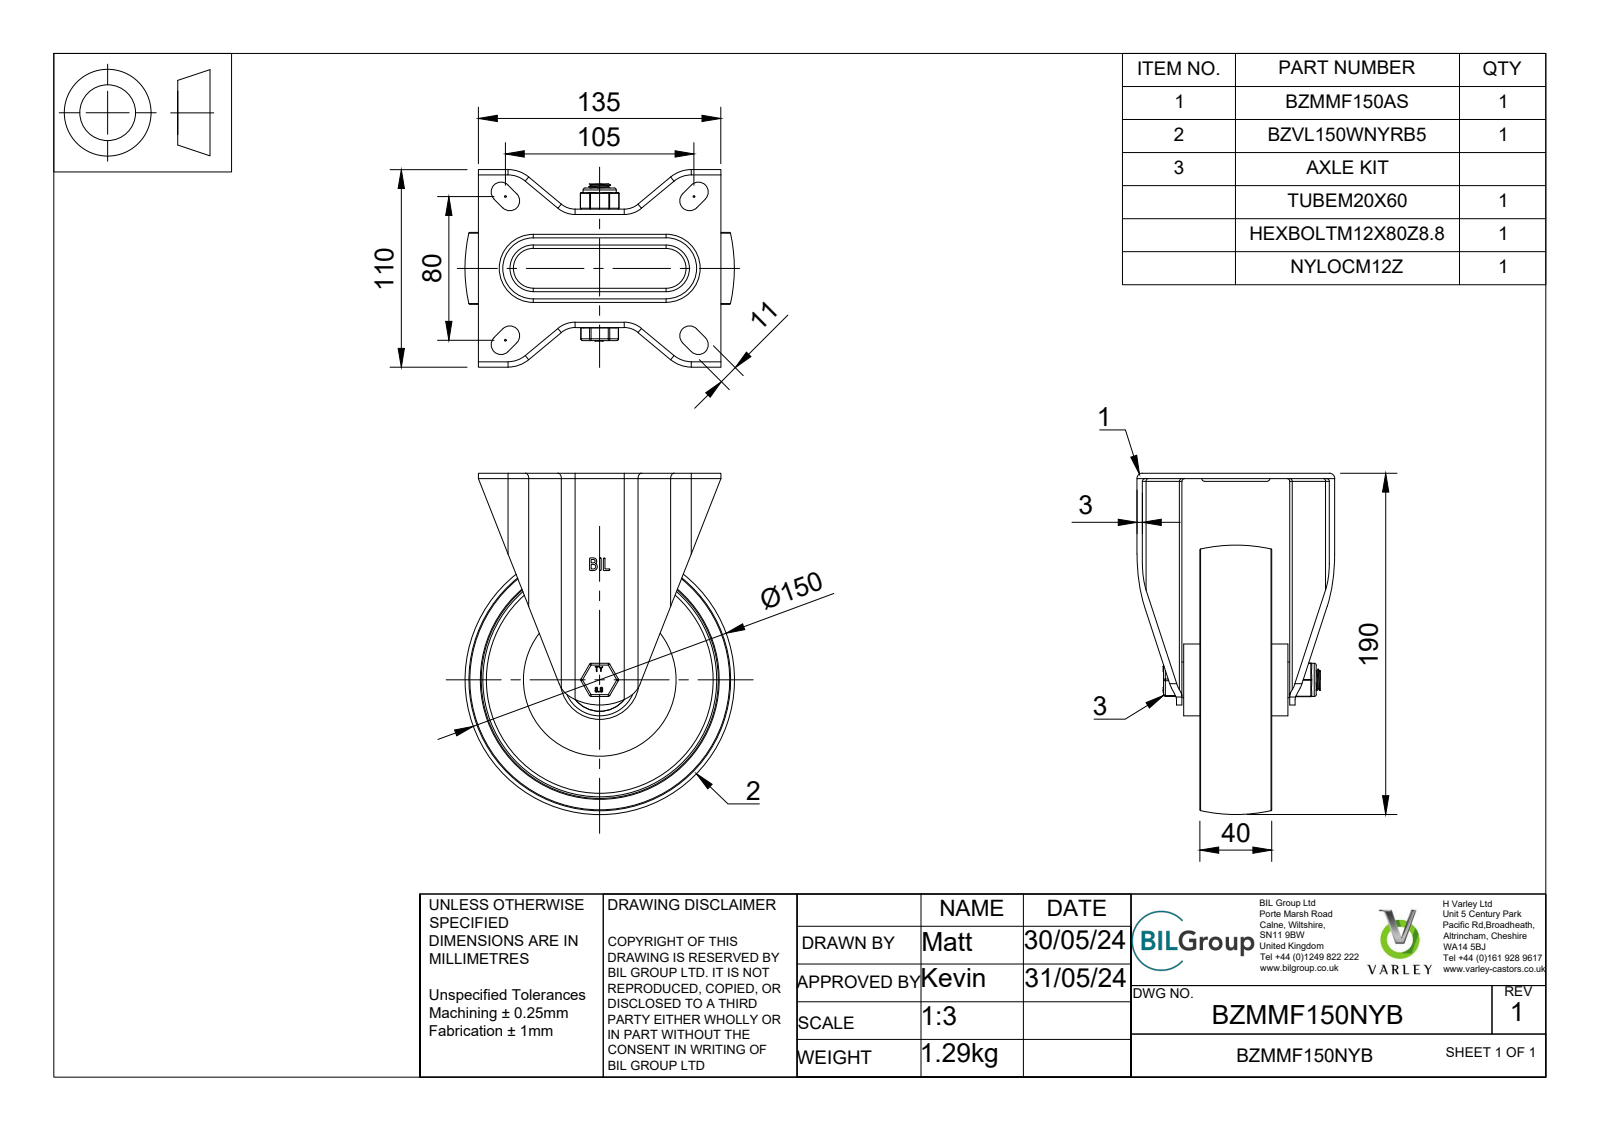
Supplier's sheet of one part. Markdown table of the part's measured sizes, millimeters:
| quantity | value |
| --- | --- |
| part name | BZMMF150NYB v4; BZMMF150AS v1; BZMMF150AS; ZINC PLATED, PRESSED STEEL BRACKET (+7 more) |
| STEP written by | Autodesk Translation Framework v13.14.0.145 (AUTOMOTIVE_DESIGN) |
| units | millimeters |
| bodies | 16 solids, 474 faces (197 planar, 171 cylindrical, 106 other) |
| overall size | 190 × 150 × 110 |
| volume | 441 554 mm³ |
| surface area | 182 962 mm² |
| round holes (diameter × count) | 12 × 1, 12.25 × 1, 12.5 × 1, 14 × 1, 20 × 1, 20.2 × 1, 35 × 1 |
| round bosses / shafts (diameter × count) | 7.5 × 8, 40 × 1, 34 × 1, 19.9 × 1, 18.5 × 1, 18 × 1, 11.83 × 1, 9.84 × 1 |
| partial cylindrical surfaces (radius × count) | 0.5 × 18, 1 × 12, 1.5 × 12, 3 × 8, 5.5 × 8, 2 × 4, 6 × 4, 9 × 4 |
| main face-to-face distances | 3, 26, 8, 29, 24.74, 34, 50, 37, 63, 13 |
